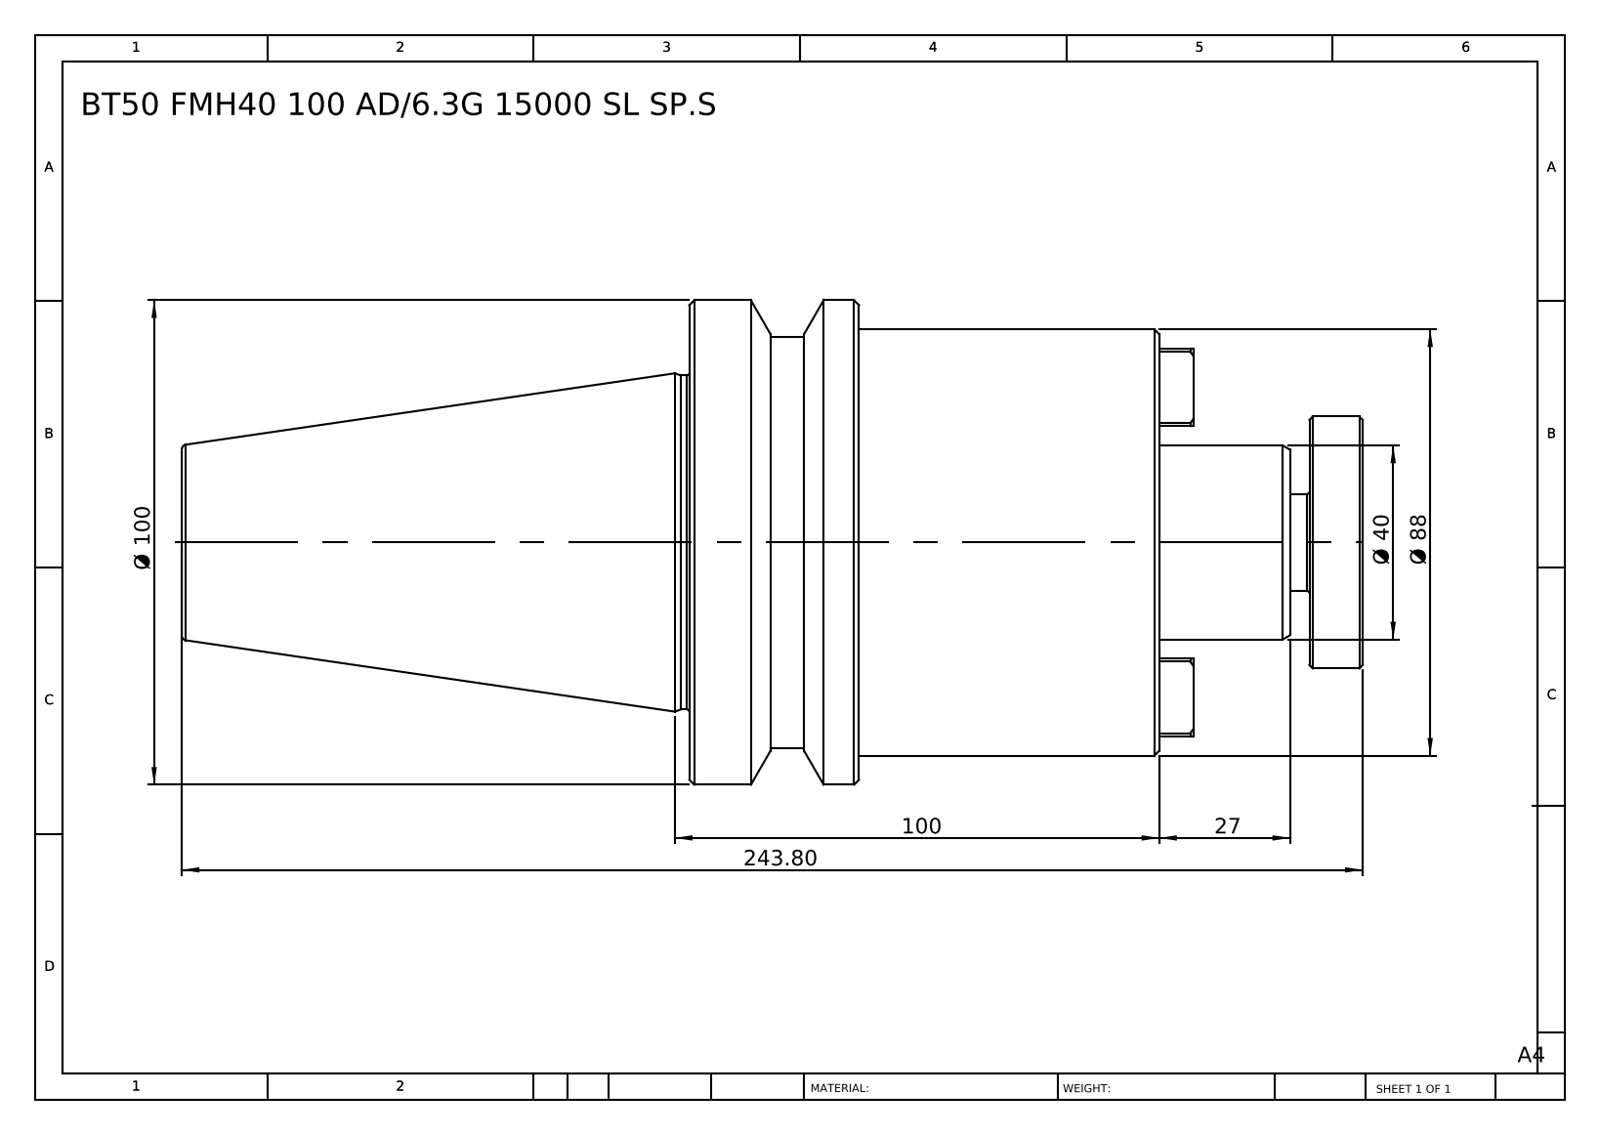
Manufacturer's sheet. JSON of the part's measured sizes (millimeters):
{"part_name": "BT50 FMH40 100 AD-6.3G 15000 SL SP.S", "step_written_by": "SolidWorks 2014 (CONFIG_CONTROL_DESIGN)", "units": "millimeters", "bodies": {"solids": 1, "faces": 77, "planar": 35, "cylindrical": 16, "other": 26}, "overall_size": [243.8, 100, 100], "volume_mm3": 949033, "surface_area_mm2": 71046, "round_bosses_or_shafts": [[100, 1], [88, 1], [85, 1], [69, 1], [52, 1], [40, 1], [20, 1]], "face_to_face_distances": [97, 42, 139, 35, 104, 11, 31, 128, 93, 62]}
